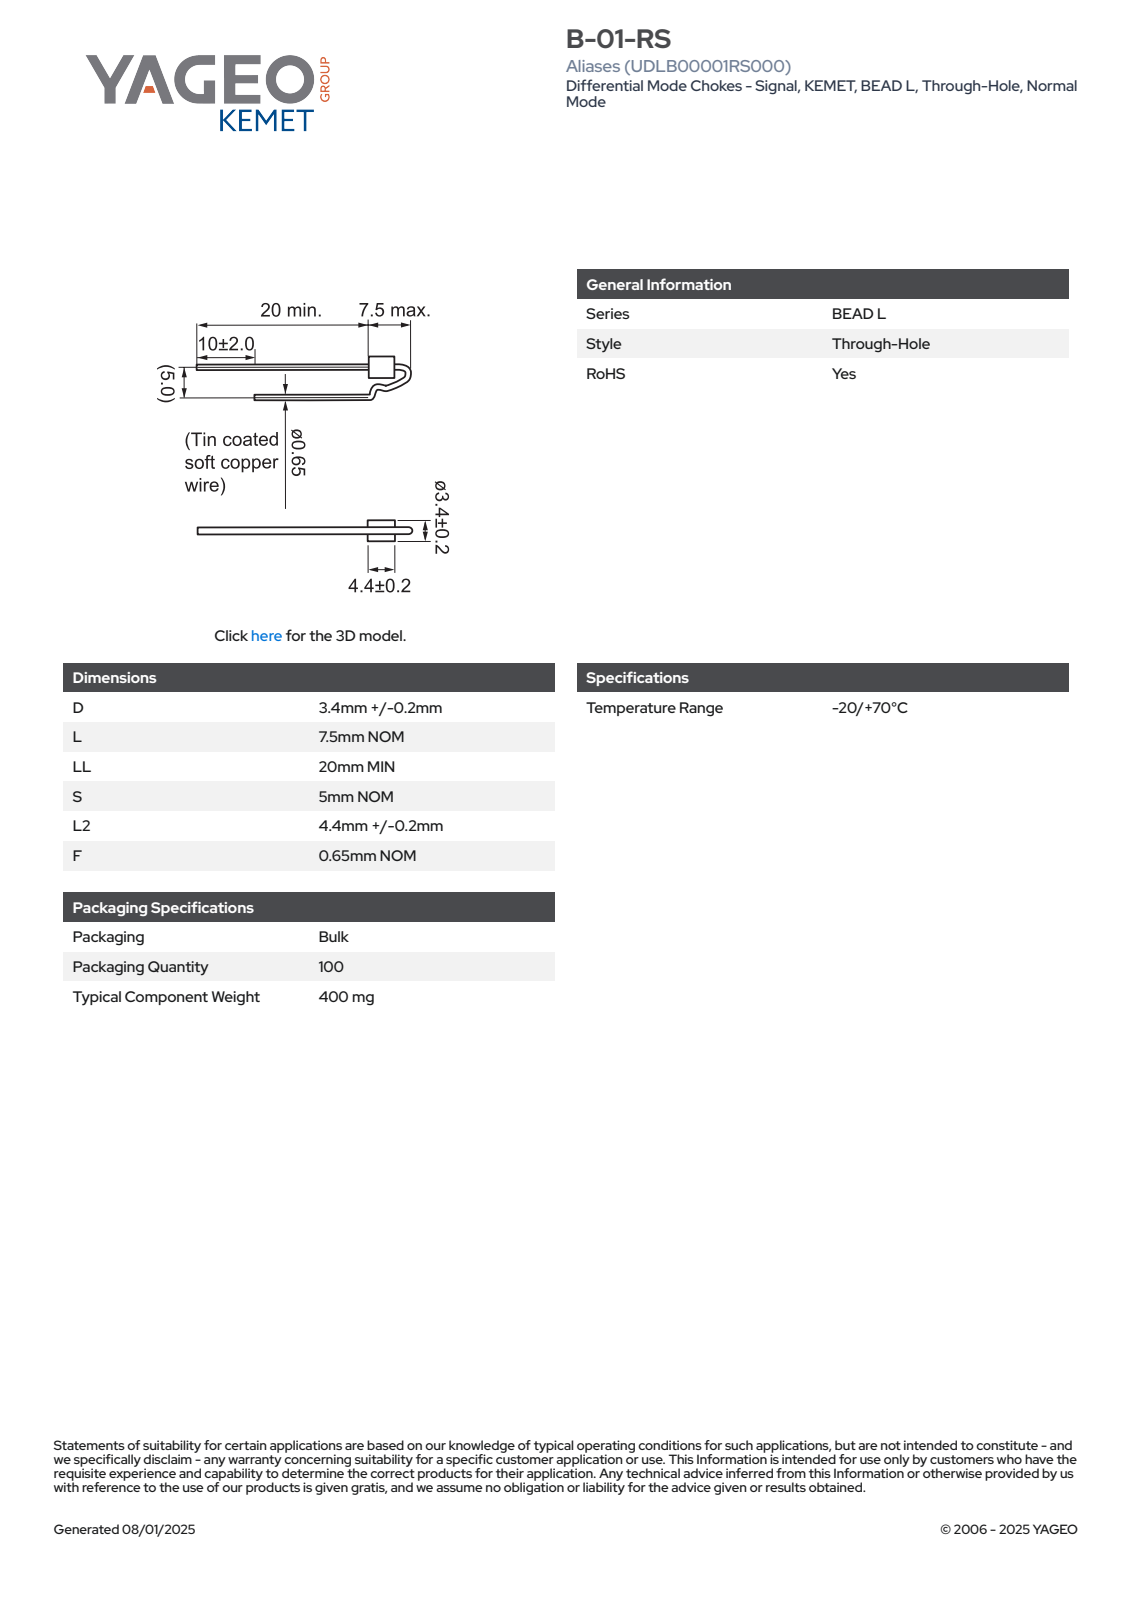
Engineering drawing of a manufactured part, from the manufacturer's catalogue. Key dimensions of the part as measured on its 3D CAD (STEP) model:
Part name (STEP PRODUCT): IL_B01RS_D3.6L7.5L24.6S5LL20LL210
STEP written by: SolidWorks 2014 (AUTOMOTIVE_DESIGN)
Units: millimetres
Bodies: 1 solid, 92 faces (26 planar, 25 cylindrical, 41 other)
Overall size (bounding box): 27.5 × 7.12 × 3.61
Volume: 61 mm³ · Surface area: 157 mm²
Round bosses / shafts (diameter × count): ⌀0.65 ×6, ⌀3.6 ×1
Partial cylindrical surfaces — rounded edges, fillets, slot ends (radius × count): R1.81 ×1
Main face-to-face distances: 4.6, 20, 24.6, 12, 8, 12.6
